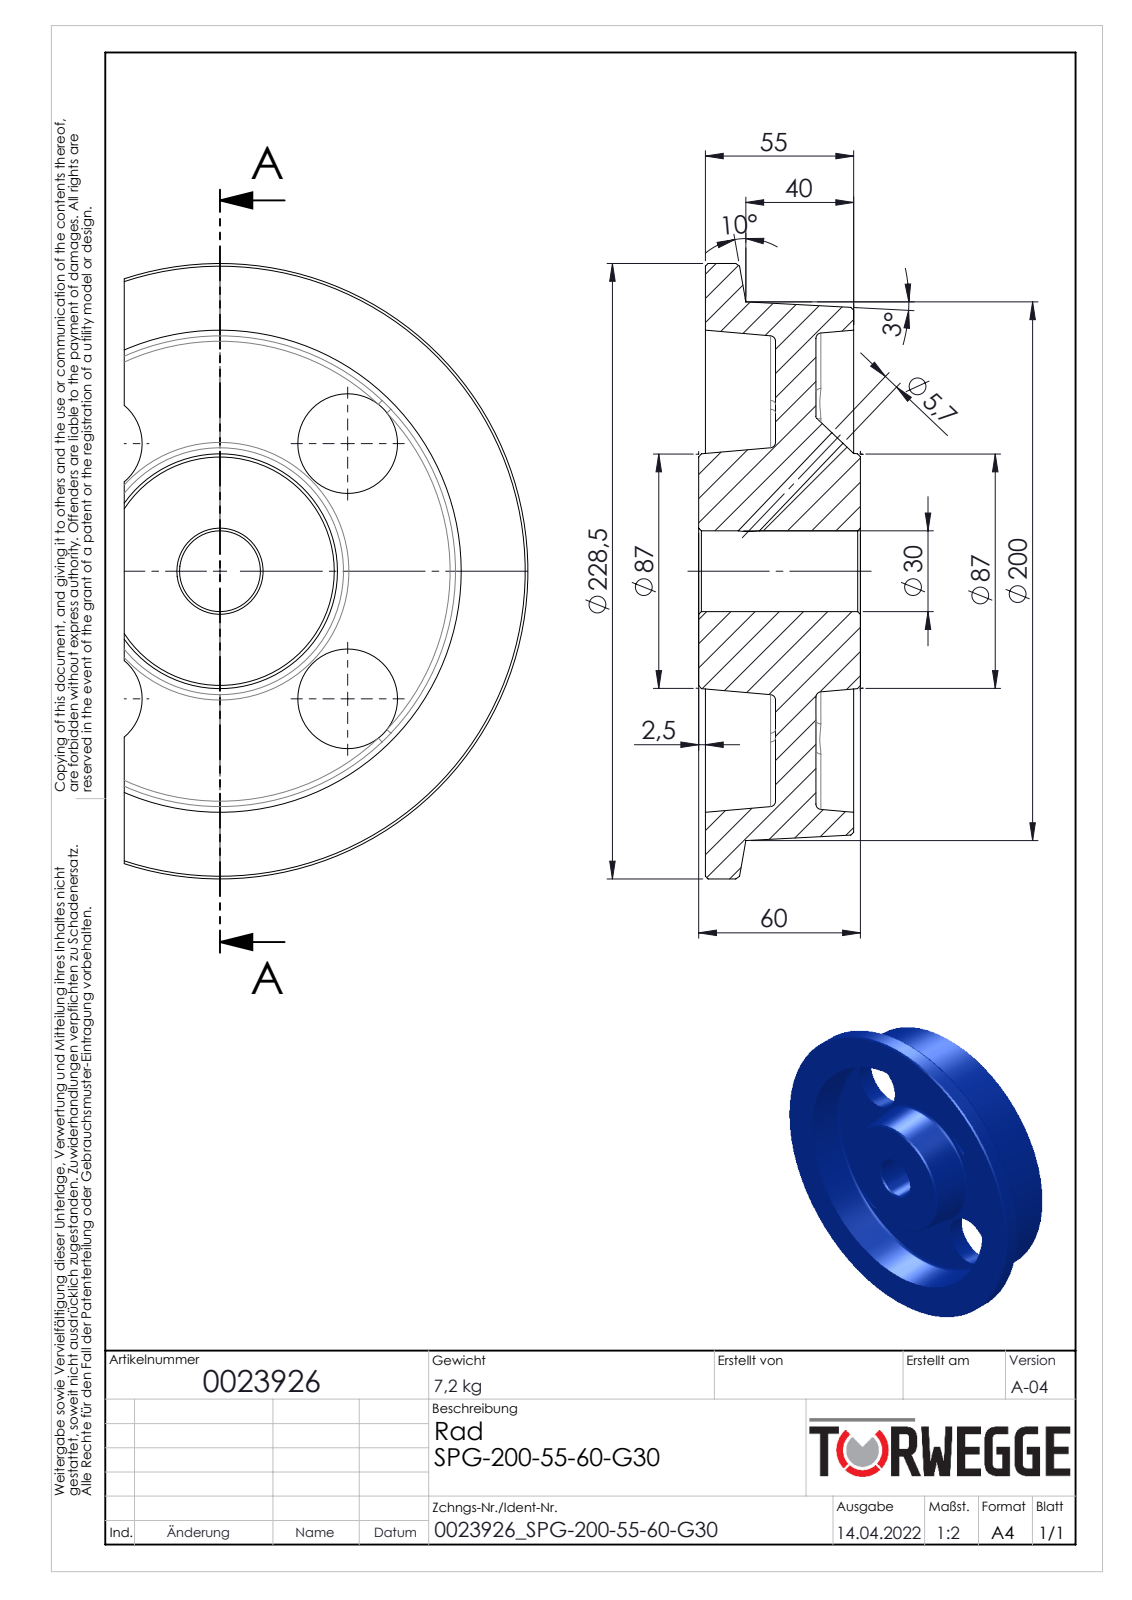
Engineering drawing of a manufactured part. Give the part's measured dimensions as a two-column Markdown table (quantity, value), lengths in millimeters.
| quantity | value |
| --- | --- |
| part name | 0023926 |
| STEP written by | SolidWorks 2020 (AUTOMOTIVE_DESIGN) |
| units | millimeters |
| bodies | 1 solid, 133 faces (12 planar, 11 cylindrical, 110 other) |
| overall size | 228.5 × 228.5 × 60 |
| volume | 1 014 000 mm³ |
| surface area | 146 720 mm² |
| round holes (diameter × count) | 5.7 × 1, 30 × 1 |
| round bosses / shafts (diameter × count) | 228.5 × 1 |
| partial cylindrical surfaces (radius × count) | 1 × 5 |
| main face-to-face distances | 26, 41, 15, 57.5, 2.5, 31.5, 16.5, 28.5, 43.5, 60 |
